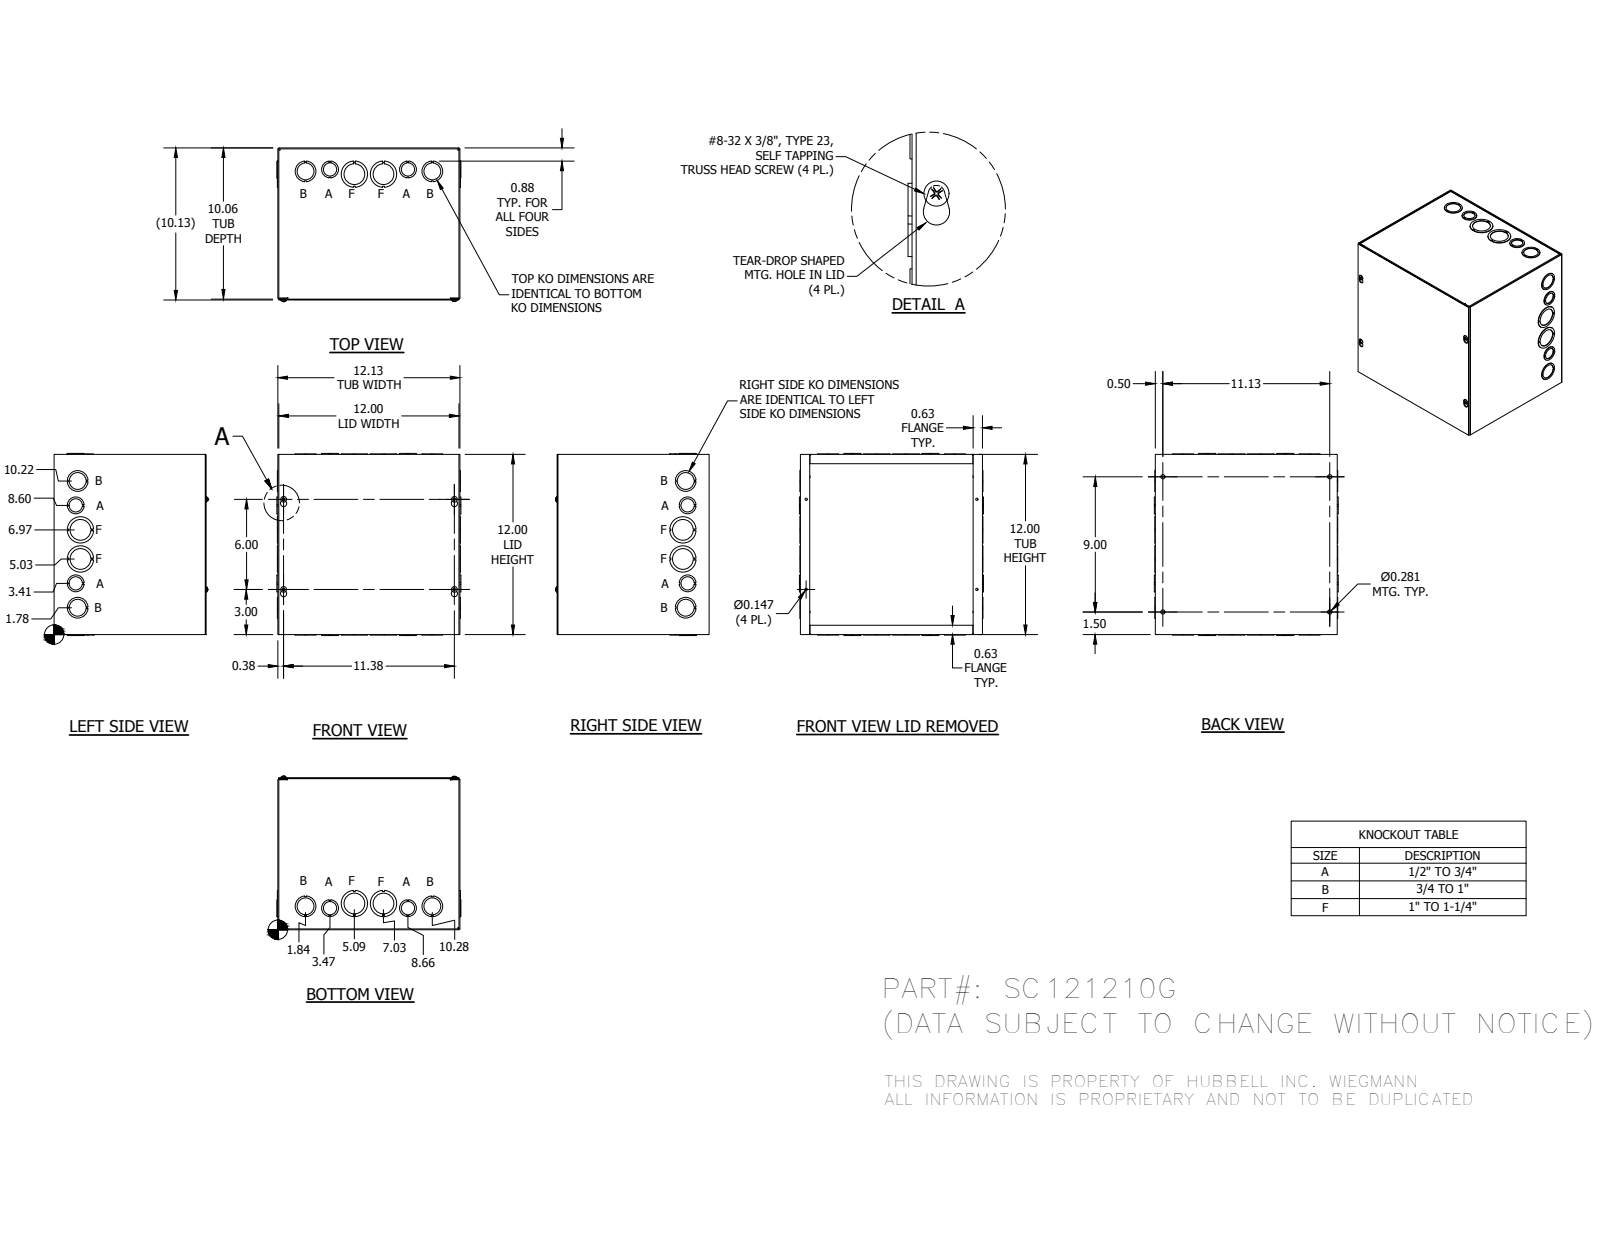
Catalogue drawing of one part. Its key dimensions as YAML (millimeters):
part_name: "SC121210GBLR; SC1210GTB; SC1212GLPA; 34056 (+1 more)"
step_written_by: "Autodesk Inventor 2014 (AUTOMOTIVE_DESIGN)"
units: millimeters
bodies: {solids: 21, faces: 943, planar: 683, cylindrical: 192, other: 68}
overall_size: [311.15, 307.98, 259.72]
round_holes:
  - {diameter: 28.57, count: 8}
  - {diameter: 34.92, count: 8}
  - {diameter: 3.73, count: 4}
  - {diameter: 7.14, count: 4}
  - {diameter: 22.22, count: 4}
  - {diameter: 44.45, count: 4}
round_bosses_or_shafts:
  - {diameter: 9.75, count: 4}
  - {diameter: 4.17, count: 4}
partial_cylinders:
  - {radius: 0.4, count: 12}
  - {radius: 1.98, count: 12}
  - {radius: 3.17, count: 4}
  - {radius: 5.16, count: 4}
face_to_face_distances: [1.59, 304.8, 303.21, 306.39, 254, 1.58, 255.59, 257.17, 255.58, 301.62]
hole_center_spacings: [38.23, 41.4, 42.03, 82.69, 90.9, 131.92, 173.13, 190.53]
